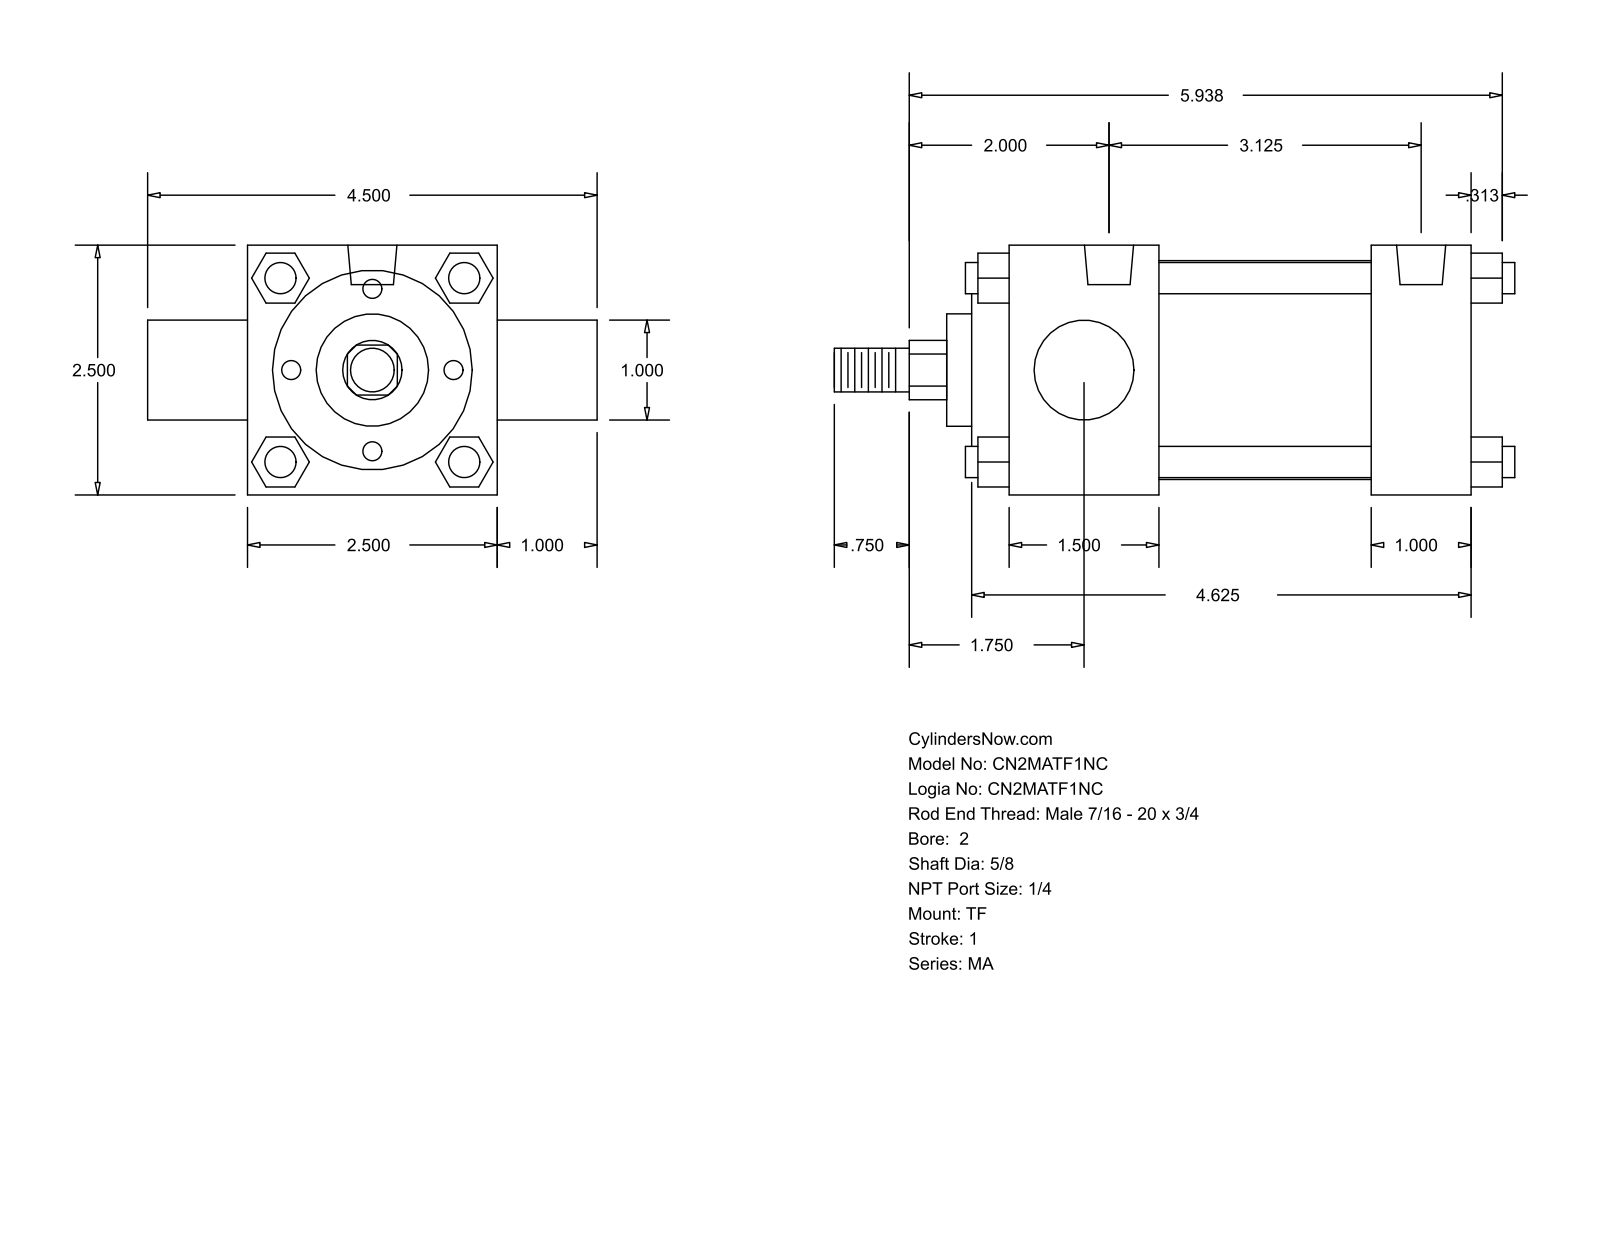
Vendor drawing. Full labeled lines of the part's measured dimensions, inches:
Part name (STEP PRODUCT): MA_TF__0200_0.625
STEP written by: GSSL Pune (CONFIG_CONTROL_DESIGN)
Units: inches
Bodies: 0 solids, 122 faces (93 planar, 29 cylindrical, 0 other)
Overall size (bounding box): 6.813 × 4.5 × 2.5
Round holes (diameter × count): ⌀0.313 ×3, ⌀0.492 ×2
Round bosses / shafts (diameter × count): ⌀0.313 ×4, ⌀2.19 ×1, ⌀2 ×1, ⌀1.125 ×1, ⌀1 ×1, ⌀0.625 ×1, ⌀0.437 ×1
Partial cylindrical surfaces — rounded edges, fillets, slot ends (radius × count): R0.297 ×1
Main face-to-face distances: 2.5, 2.125, 1.5, 0.5, 4.625, 3.625, 3.125, 1, 0.375, 1.875
Hole centre spacings: 3.125
